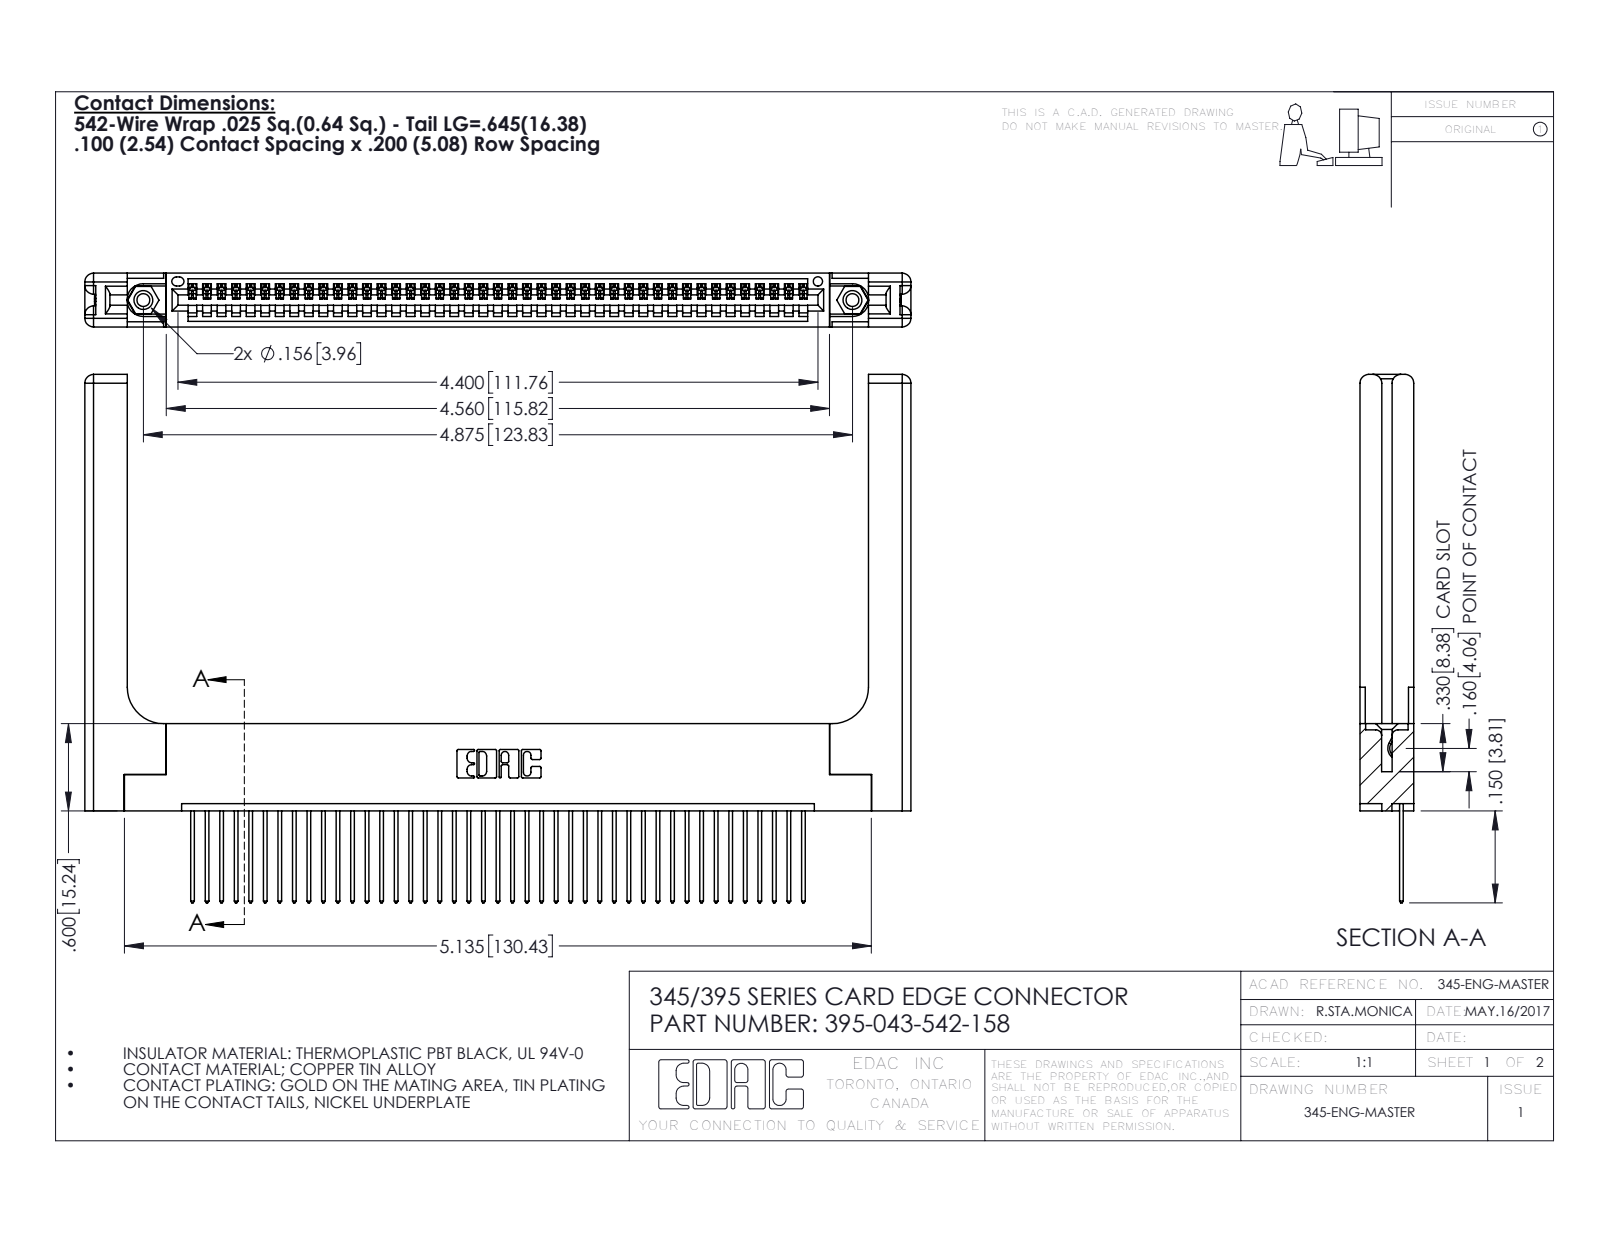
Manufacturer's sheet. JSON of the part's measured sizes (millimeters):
{"part_name": "395-043-542-158; 345-220-058_345-220-058; 345-292-001_345-293-142; 345 Part_Flush Mounting Lugs - 0.156 Dia-TH (+1 more)", "step_written_by": "SolidWorks 2016 (CONFIG_CONTROL_DESIGN)", "units": "millimeters", "bodies": {"solids": 48, "faces": 2876, "planar": 1948, "cylindrical": 868, "other": 60}, "overall_size": [144.2, 92.3, 9.4], "volume_mm3": 22300, "surface_area_mm2": 24270, "round_holes": [[2.3, 2], [3.2, 2], [4, 2], [1.6, 1]], "round_bosses_or_shafts": [[3.9, 2]], "partial_cylinders_radius": [[0.2, 86], [0.3, 86], [0.3, 22], [1.5, 16], [0.2, 6], [0.8, 6], [0.7, 3], [0.8, 2]], "face_to_face_distances": [1.8, 9.4, 7.6, 2.5, 6.9, 0.6, 5.1, 5.7, 3.8, 3.8], "hole_center_spacings": [6.9, 117.8, 123.8]}
